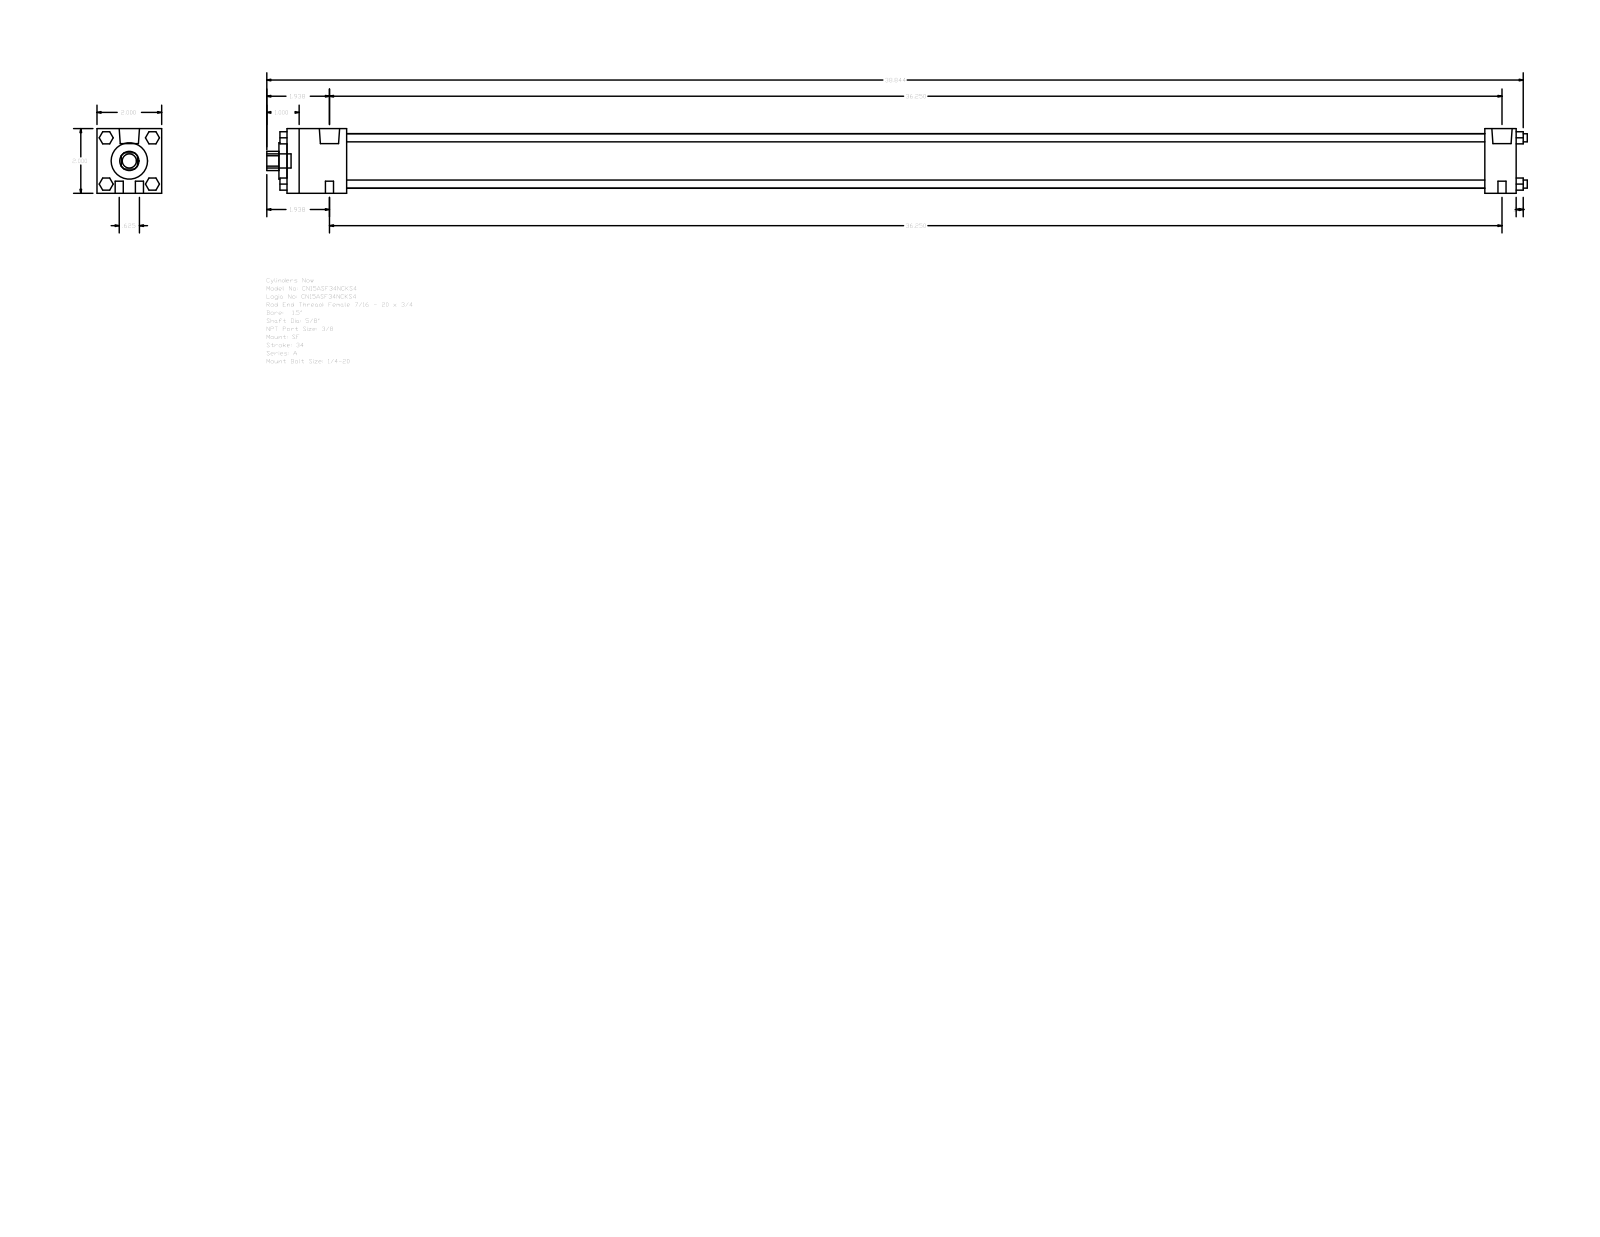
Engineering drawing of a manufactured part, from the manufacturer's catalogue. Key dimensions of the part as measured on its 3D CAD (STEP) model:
Part name (STEP PRODUCT): A_SF__0150_0.625
STEP written by: GSSL Pune (CONFIG_CONTROL_DESIGN)
Units: millimetres
Bodies: 0 solids, 124 faces (94 planar, 30 cylindrical, 0 other)
Overall size (bounding box): 989.81 × 50.8 × 50.8
Round holes (diameter × count): ⌀15.88 ×1, ⌀28.57 ×1, ⌀42.93 ×1
Round bosses / shafts (diameter × count): ⌀6.35 ×8, ⌀15.93 ×2, ⌀5.56 ×2, ⌀11.11 ×1
Partial cylindrical surfaces — rounded edges, fillets, slot ends (radius × count): R7.54 ×1
Main face-to-face distances: 50.8, 965.2, 46.83, 940.59, 893.76, 918.37, 24.61, 9.52, 6.35, 53.18
